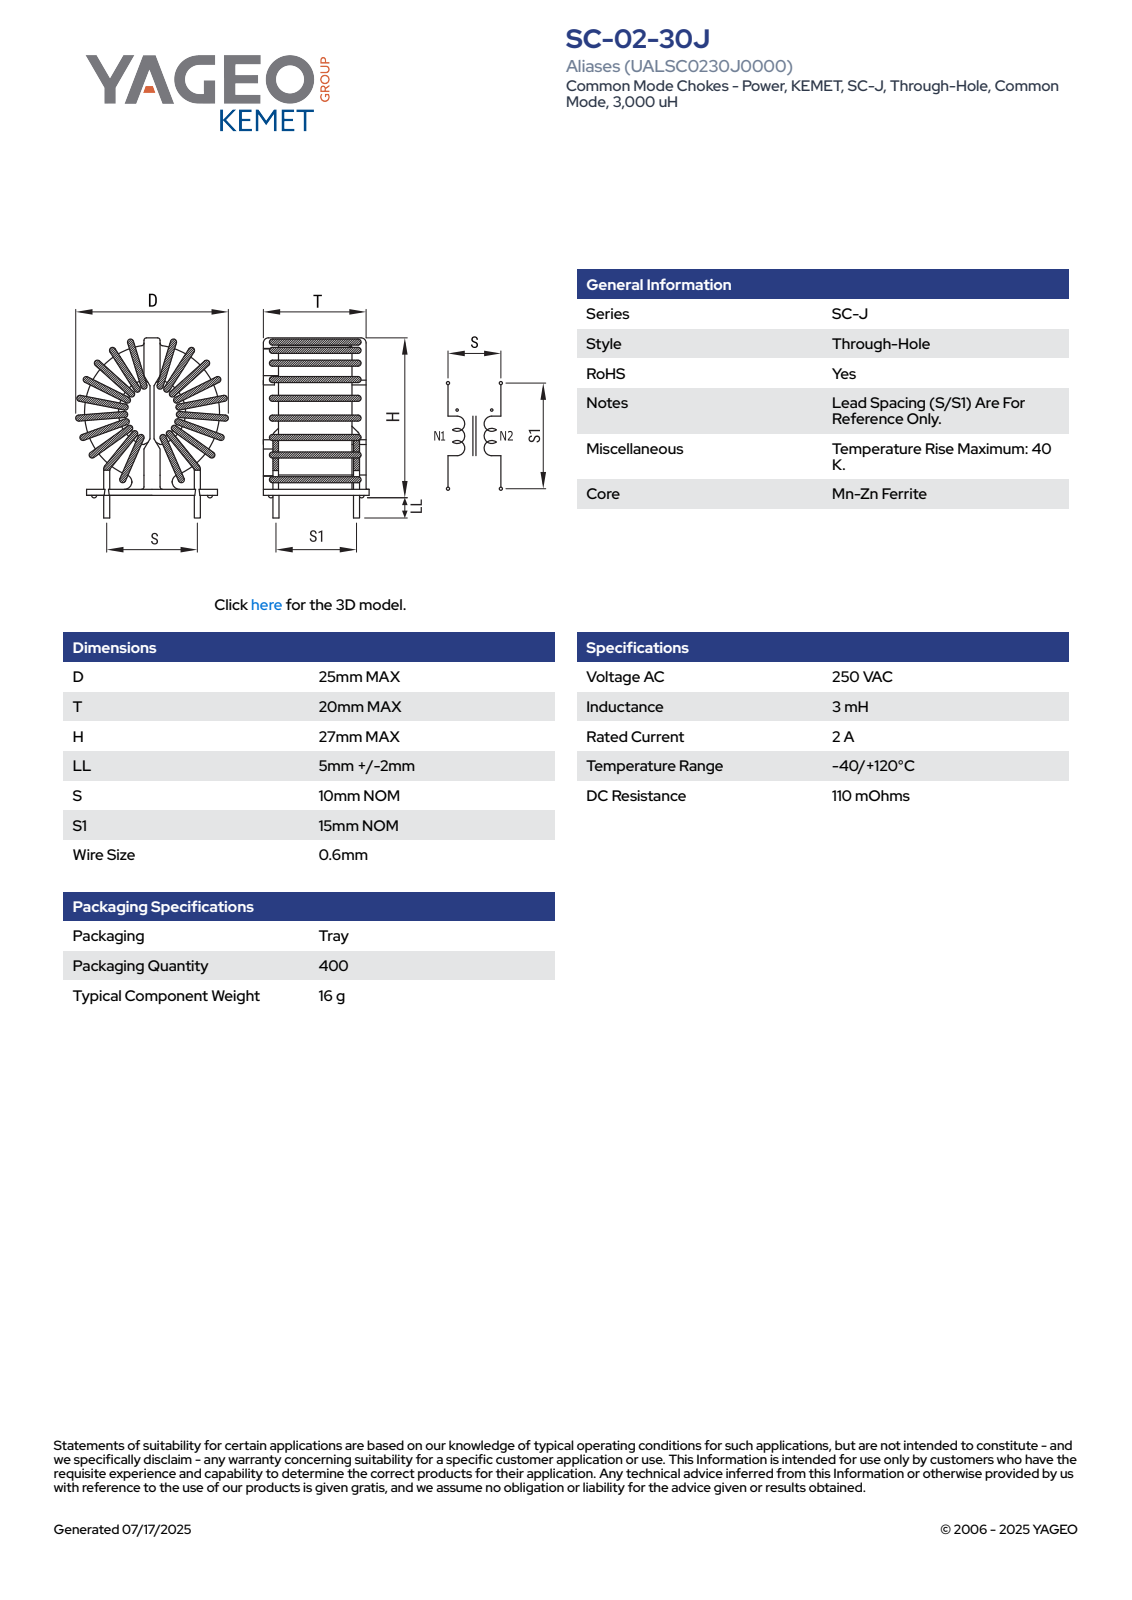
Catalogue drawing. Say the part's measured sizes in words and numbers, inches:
The part is named "SC-02-30J". Its 3-D file was written by "SolidWorks 2018 (AUTOMOTIVE_DESIGN)". It is 1 solid with 334 faces: 141 planar, 113 cylindrical and 80 other. Overall it measures 1.24 by 0.984 by 0.787 inches. Its volume is 0.552 cubic inches and its surface area 7.301 square inches. Round bosses or shafts: 8 of diameter 0.024, 4 of diameter 0.039. Partial cylindrical surfaces (rounded edges, fillets, slot ends): 21 of radius 0.02, 16 of radius 0.012, 6 of radius 0.039, 4 of radius 0.017, 4 of radius 0.059, 2 of radius 0.035, 1 of radius 0.122, 1 of radius 0.173. The main face-to-face distances are 0.093, 0.748, 0.047, 0.079, 0.126, 0.031, 0.496, 0.02, 0.768, 0.37.
